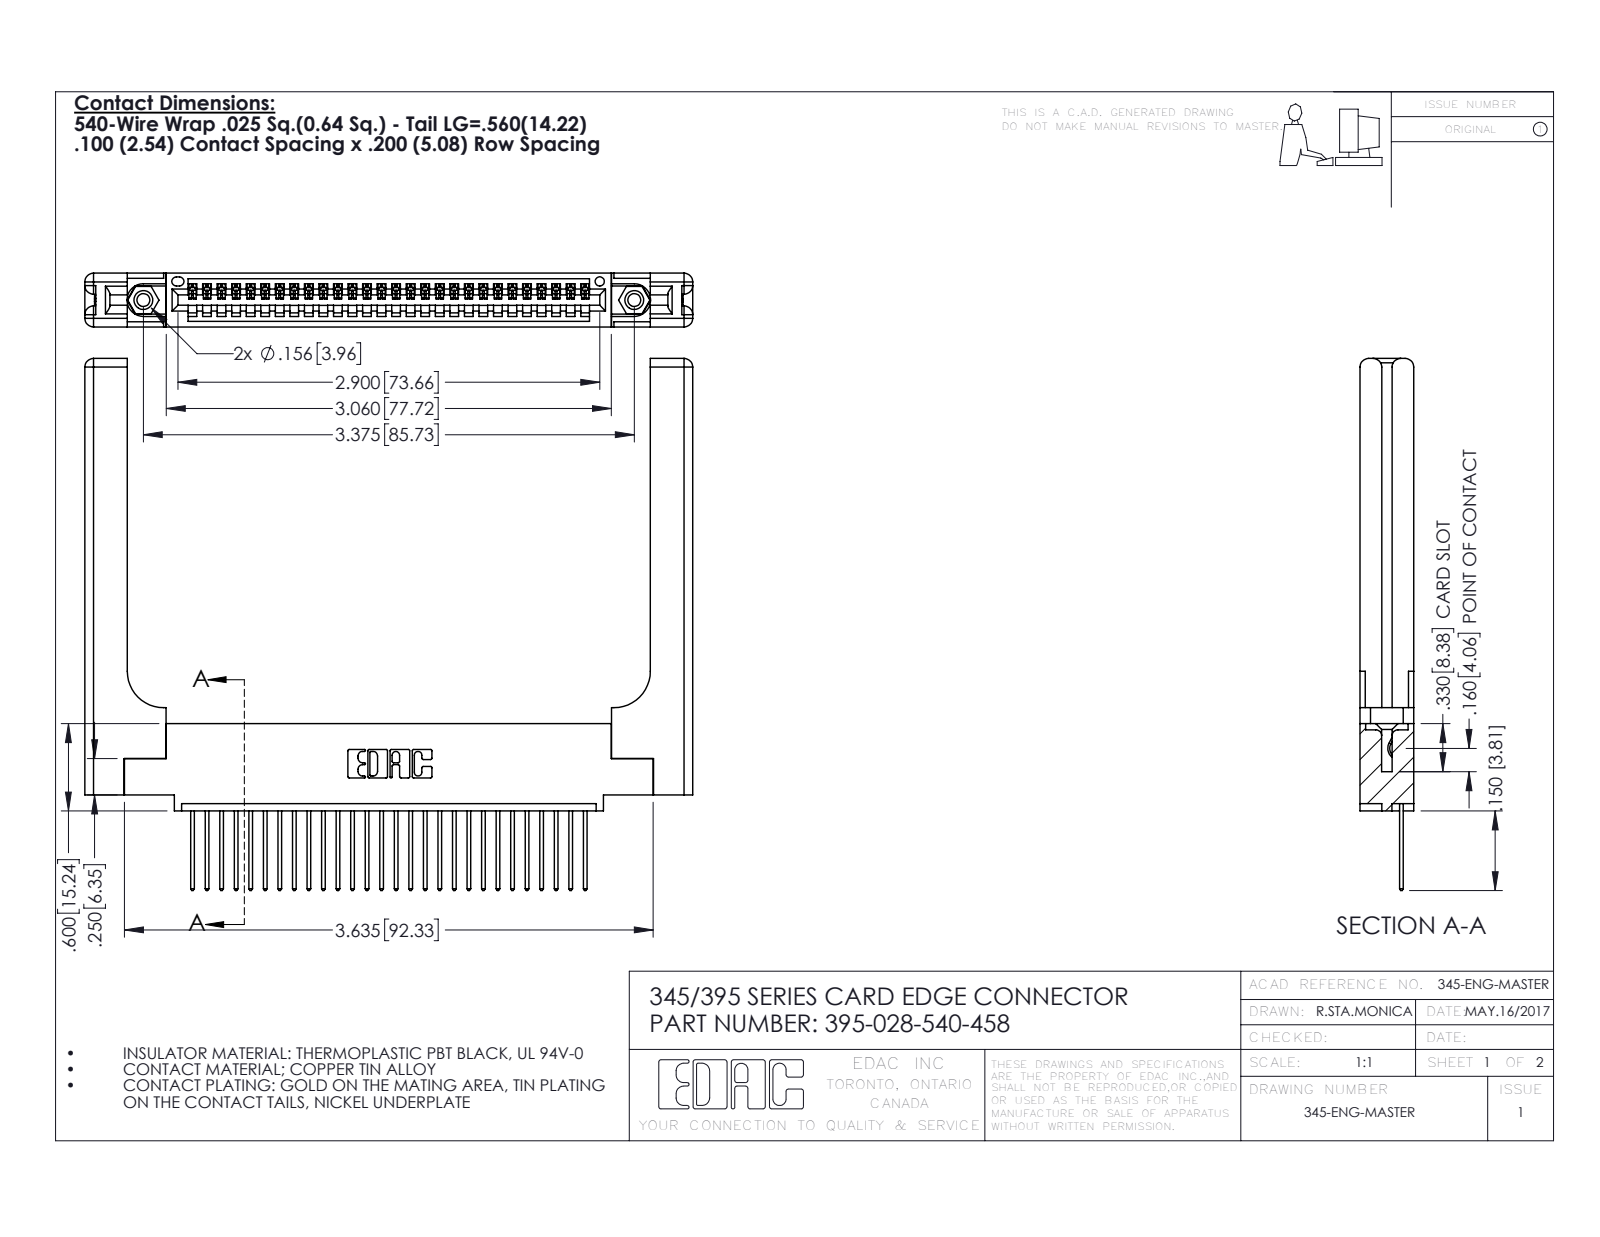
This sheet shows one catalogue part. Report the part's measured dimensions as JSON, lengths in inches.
{"part_name": "345 Part_0.110 Offset - 0.156 Dia-TH; 345-250-001_345-250-001-102; 345-220-058_345-220-058; 395-028-540-458 (+1 more)", "step_written_by": "SolidWorks 2016 (CONFIG_CONTROL_DESIGN)", "units": "inches", "bodies": {"solids": 33, "faces": 2010, "planar": 1352, "cylindrical": 598, "other": 60}, "overall_size": [4.179, 3.657, 0.37], "volume_in3": 1.125, "surface_area_in2": 28.94, "round_holes": [[0.089, 2], [0.125, 2], [0.156, 2], [0.064, 1]], "round_bosses_or_shafts": [[0.155, 2]], "partial_cylinders_radius": [[0.006, 56], [0.01, 56], [0.01, 22], [0.06, 16], [0.007, 6], [0.031, 6], [0.026, 3], [0.03, 2]], "face_to_face_distances": [0.37, 0.072, 0.298, 0.098, 0.272, 0.025, 0.2, 0.148, 0.15, 0.077], "hole_center_spacings": [0.27, 3.14, 3.375]}
